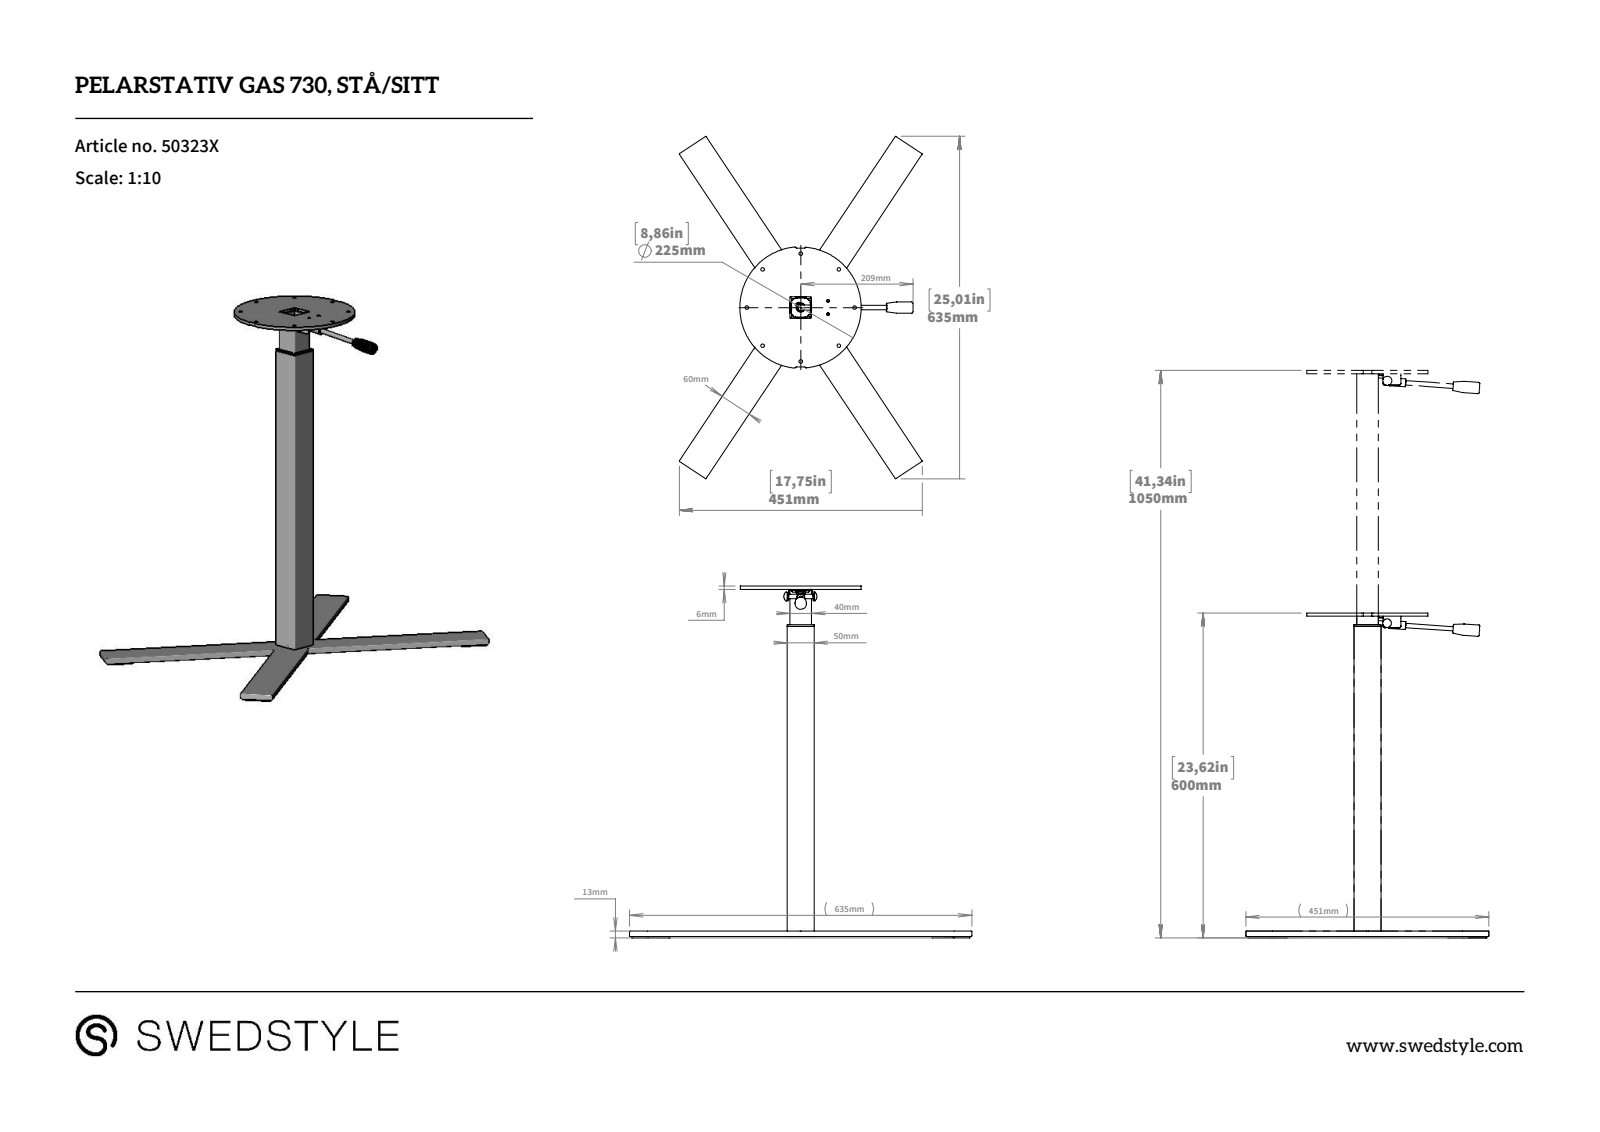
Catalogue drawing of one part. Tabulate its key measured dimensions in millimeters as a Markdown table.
| quantity | value |
| --- | --- |
| part name | 50323x_Pelarstativ 730, spak, Stå_Sitt |
| STEP written by | SolidWorks 2017 (CONFIG_CONTROL_DESIGN) |
| units | millimeters |
| bodies | 0 solids, 292 faces (115 planar, 129 cylindrical, 48 other) |
| overall size | 702.45 × 634.89 × 450.96 |
| round holes (diameter × count) | 6.6 × 12, 3.4 × 4, 5 × 2, 15.3 × 1 |
| round bosses / shafts (diameter × count) | 8 × 2, 225 × 1, 21 × 1, 15 × 1 |
| partial cylindrical surfaces (radius × count) | 2 × 24, 1 × 22, 0.5 × 8, 2.5 × 8, 3 × 6, 2.75 × 4, 4 × 2, 6 × 1 |
| main face-to-face distances | 2, 5, 45, 7, 43, 38, 10, 50, 40, 36 |
| hole center spacings | 76.54, 84.72, 100, 102.85, 118.23, 141.42, 184.78, 24.04 |
